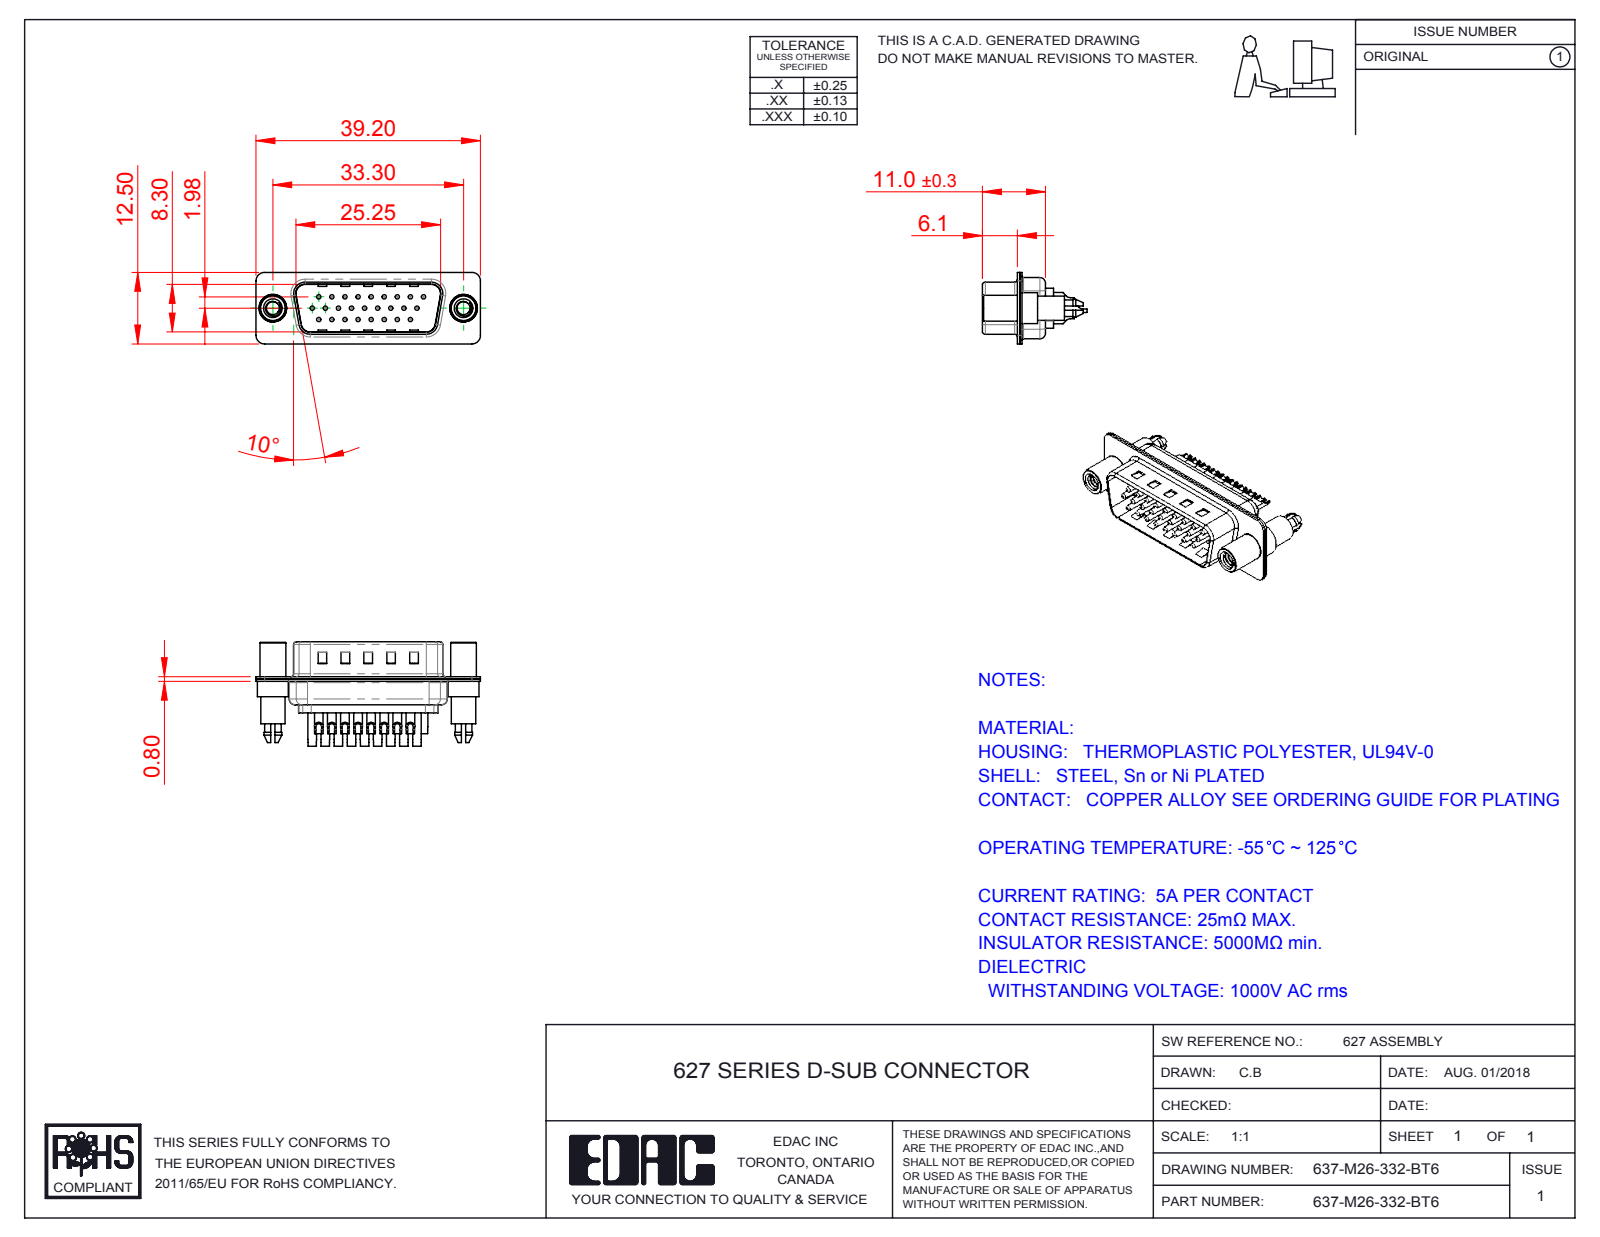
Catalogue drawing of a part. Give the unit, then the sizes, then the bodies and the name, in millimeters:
Units: millimetres
Overall size (bounding box): 39.2 × 18.25 × 12.5
Round holes (diameter × count): ⌀0.75 ×26, ⌀1 ×26, ⌀1.6 ×26, ⌀2 ×26, ⌀2.26 ×2, ⌀4 ×2, ⌀4.8 ×2
Round bosses / shafts (diameter × count): ⌀1.5 ×26, ⌀5.4 ×2, ⌀4.9 ×2, ⌀4.5 ×2, ⌀4.25 ×2
Partial cylindrical surfaces — rounded edges, fillets, slot ends (radius × count): R1.5 ×18, R2 ×12, R1.6 ×10, R0.5 ×8, R1 ×7, R0.25 ×4, R0.6 ×4, R0.65 ×4
Main face-to-face distances: 0.4, 0.8, 9.5, 9.1, 8.7, 9.9, 0.75, 0.35, 1.2, 1.9
Hole centre spacings: 3.96, 2.28, 4.57, 6.05, 2.29, 8.24, 6.86, 10.48
Volume: 2 333 mm³ · Surface area: 6 558 mm²
Bodies: 31 solids, 1386 faces (411 planar, 585 cylindrical, 390 other)
Part name (STEP PRODUCT): 637M Shell Rear_26 Contacts; 637M Contact Row 2_32; 637-M26-332-BT6; 637M Shell Front_26 Contacts (+4 more)
STEP written by: SolidWorks 2016 (CONFIG_CONTROL_DESIGN)
